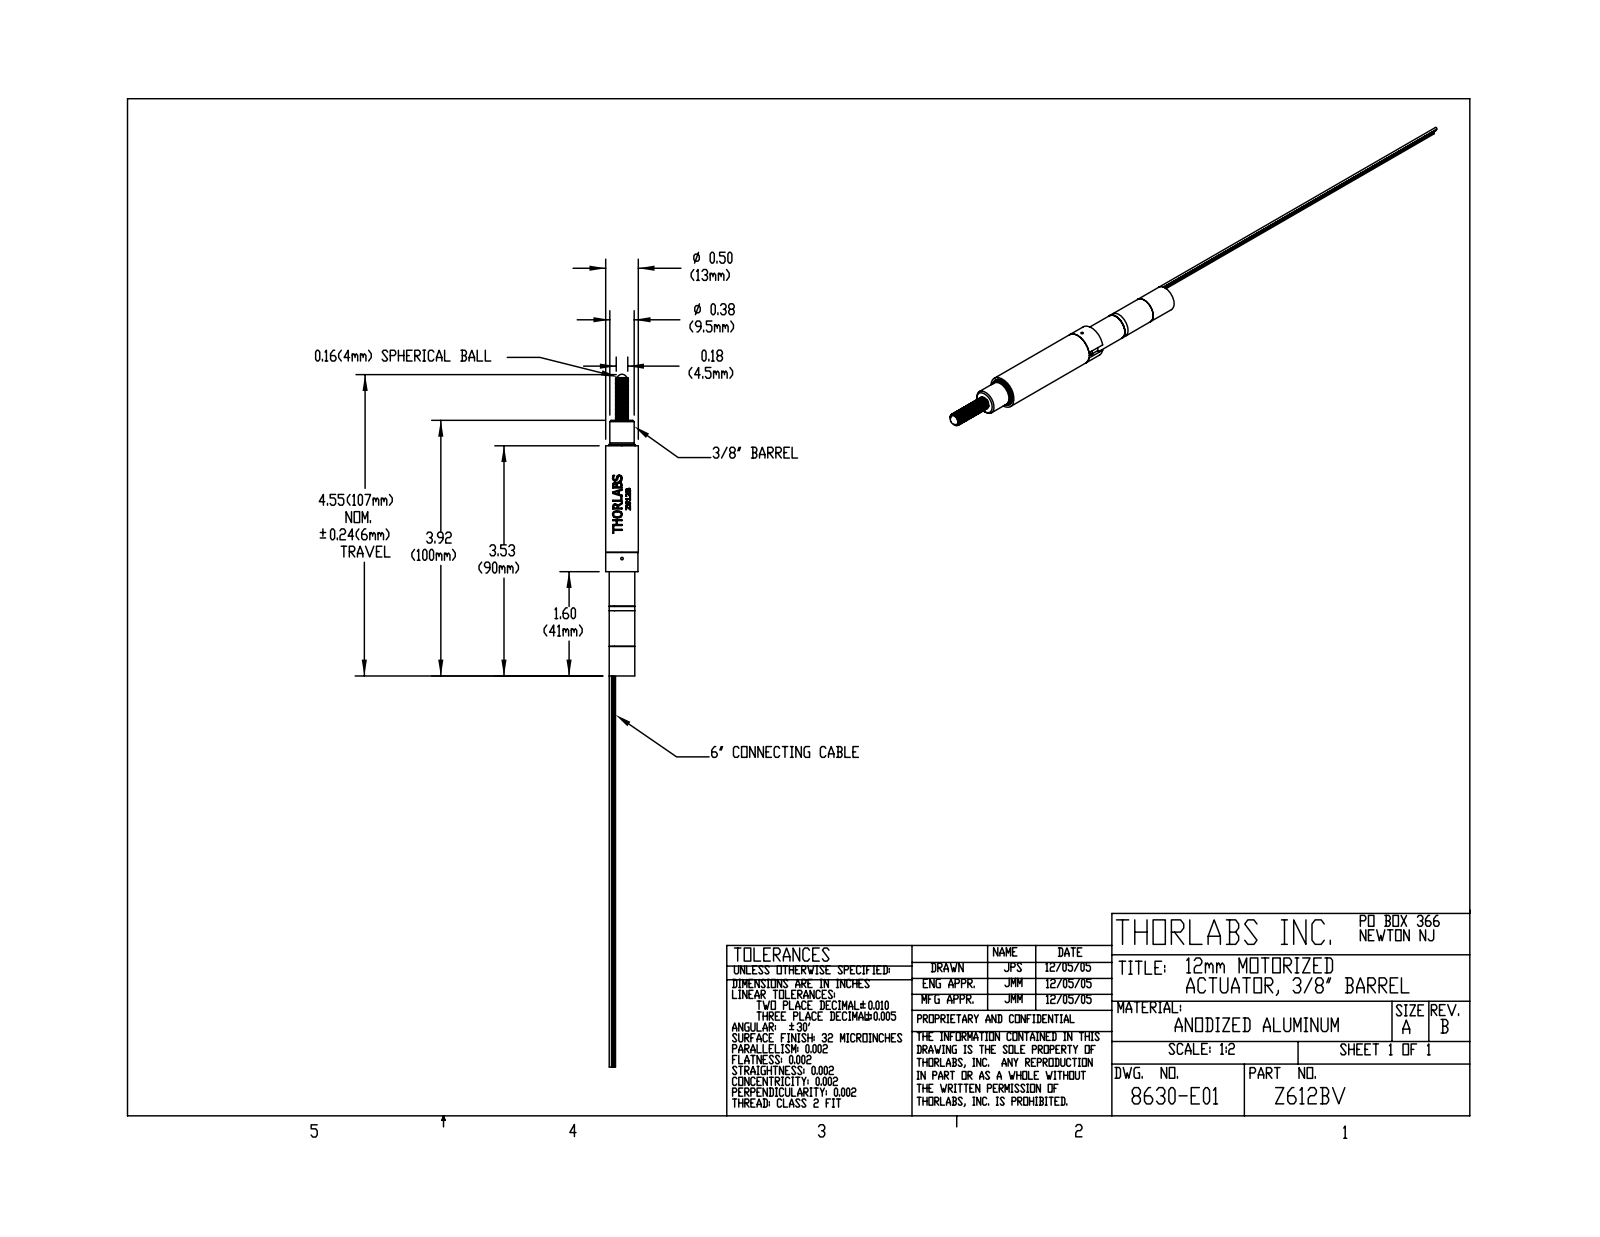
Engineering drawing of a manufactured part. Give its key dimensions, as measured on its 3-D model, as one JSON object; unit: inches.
{"part_name": "8630-E0W", "step_written_by": "SolidWorks 2007 (AUTOMOTIVE_DESIGN)", "units": "inches", "bodies": {"solids": 0, "faces": 182, "planar": 23, "cylindrical": 147, "other": 12}, "overall_size": [10.627, 0.5, 0.5], "round_holes": [[0.038, 1], [0.156, 1], [0.375, 1], [0.48, 1]], "round_bosses_or_shafts": [[0.5, 1], [0.403, 1], [0.394, 1], [0.394, 1], [0.36, 1], [0.197, 1]], "partial_cylinders_radius": [[0.017, 6], [0.063, 2]], "face_to_face_distances": [0.453, 0.618, 1.071, 0.589, 1.207, 1.66, 1.87, 2.459, 3.077, 3.53]}
